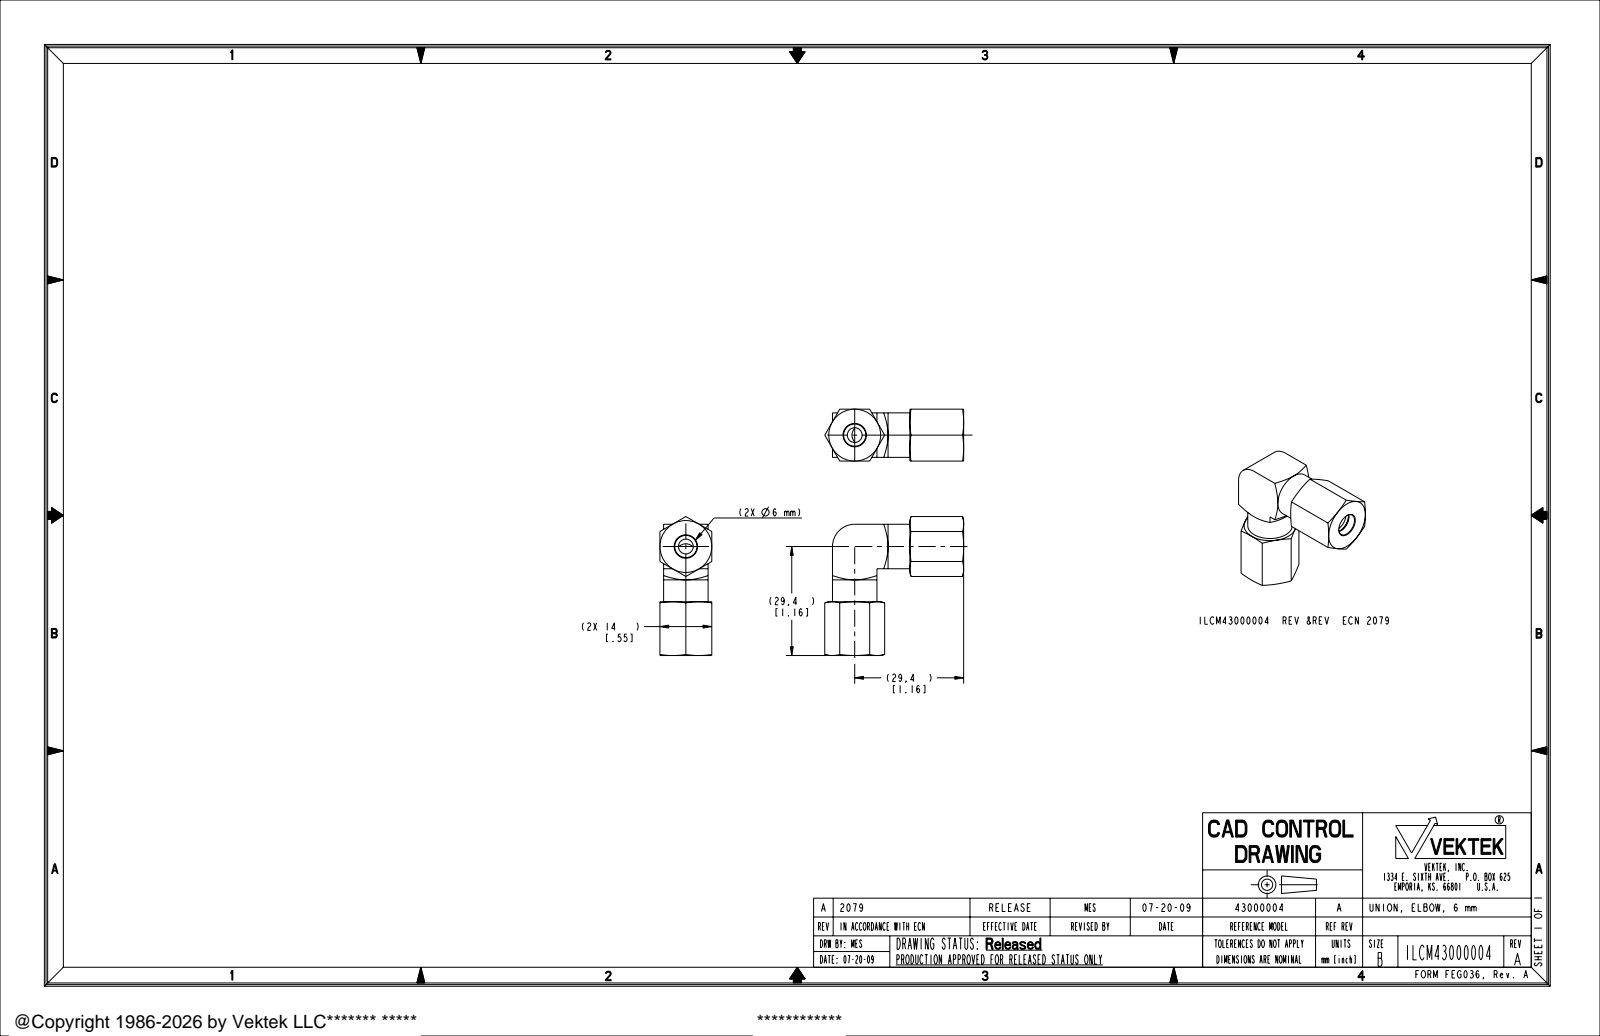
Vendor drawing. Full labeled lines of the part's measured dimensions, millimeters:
Part name (STEP PRODUCT): ILCM43000004
STEP written by: PRO/ENGINEER BY PARAMETRIC TECHNOLOGY CORPORATION, 2007460 (AUTOMOTIVE_DESIGN_CC2)
Units: millimetres
Bodies: 1 solid, 131 faces (32 planar, 33 cylindrical, 66 other)
Overall size (bounding box): 37.5 × 37.5 × 14
Volume: 7 130 mm³ · Surface area: 5 000 mm²
Round holes (diameter × count): ⌀4 ×2, ⌀6 ×2, ⌀10.4 ×2
Round bosses / shafts (diameter × count): ⌀12 ×2, ⌀9.5 ×2, ⌀8.1 ×2
Partial cylindrical surfaces — rounded edges, fillets, slot ends (radius × count): R6 ×1
Main face-to-face distances: 14, 13, 1, 12, 35.4, 14.5, 20.9, 23.4, 8.9, 10.4
